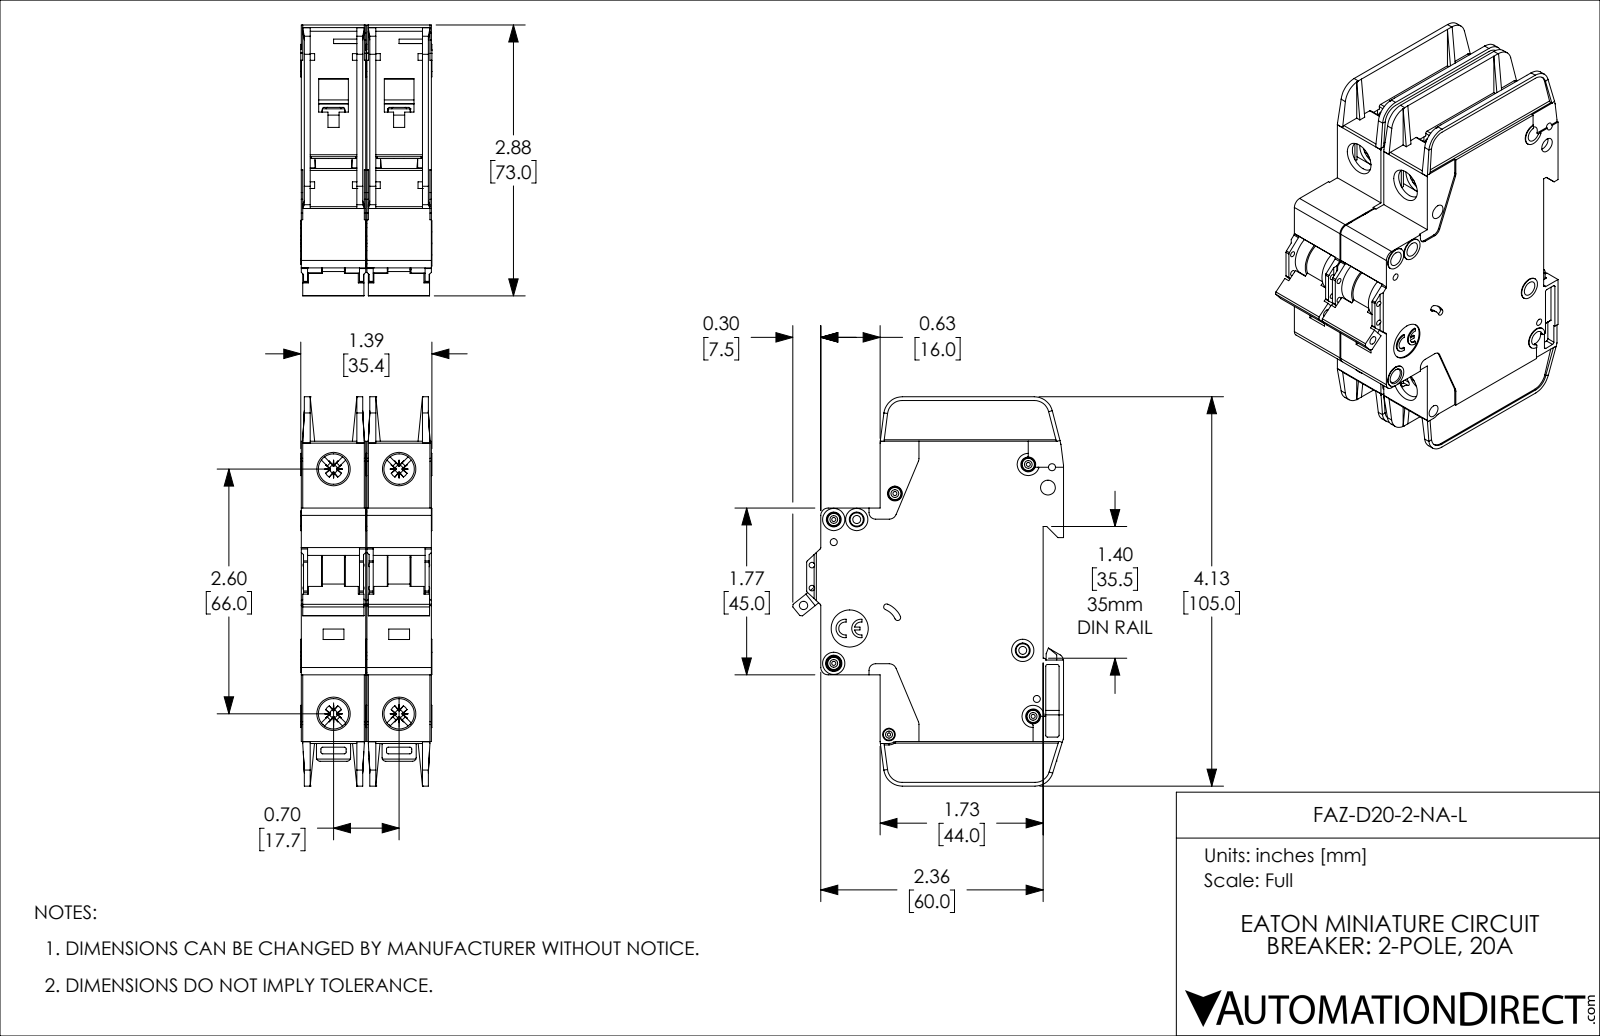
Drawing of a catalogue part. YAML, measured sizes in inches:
part_name: "FAZ-D20-2-NA-L"
step_written_by: "SolidWorks 2019 (AUTOMOTIVE_DESIGN)"
units: inches
bodies: {solids: 2, faces: 2254, planar: 1342, cylindrical: 714, other: 198}
overall_size: [4.134, 2.876, 1.394]
volume: 9.365
surface_area: 82.01
round_holes:
  - {diameter: 0.157, count: 8}
  - {diameter: 0.043, count: 5}
  - {diameter: 0.075, count: 4}
  - {diameter: 0.323, count: 4}
  - {diameter: 0.059, count: 2}
  - {diameter: 0.085, count: 2}
  - {diameter: 0.035, count: 1}
  - {diameter: 0.089, count: 1}
  - {diameter: 0.098, count: 1}
  - {diameter: 0.134, count: 1}
  - {diameter: 0.394, count: 1}
round_bosses_or_shafts:
  - {diameter: 0.13, count: 5}
  - {diameter: 0.236, count: 4}
  - {diameter: 0.118, count: 3}
  - {diameter: 0.098, count: 2}
partial_cylinders:
  - {radius: 0.02, count: 57}
  - {radius: 0.016, count: 20}
  - {radius: 0.039, count: 14}
  - {radius: 0.079, count: 10}
  - {radius: 0.043, count: 8}
  - {radius: 0.008, count: 5}
  - {radius: 0.197, count: 5}
  - {radius: 0.01, count: 4}
face_to_face_distances: [0.697, 0.047, 0.685, 0.591, 0.094, 0.638, 0.543, 1.382, 0.744, 0.65]
hole_center_spacings: [0.244, 0.537, 0.697, 0.87, 2.598, 2.69, 0.189, 0.199]
